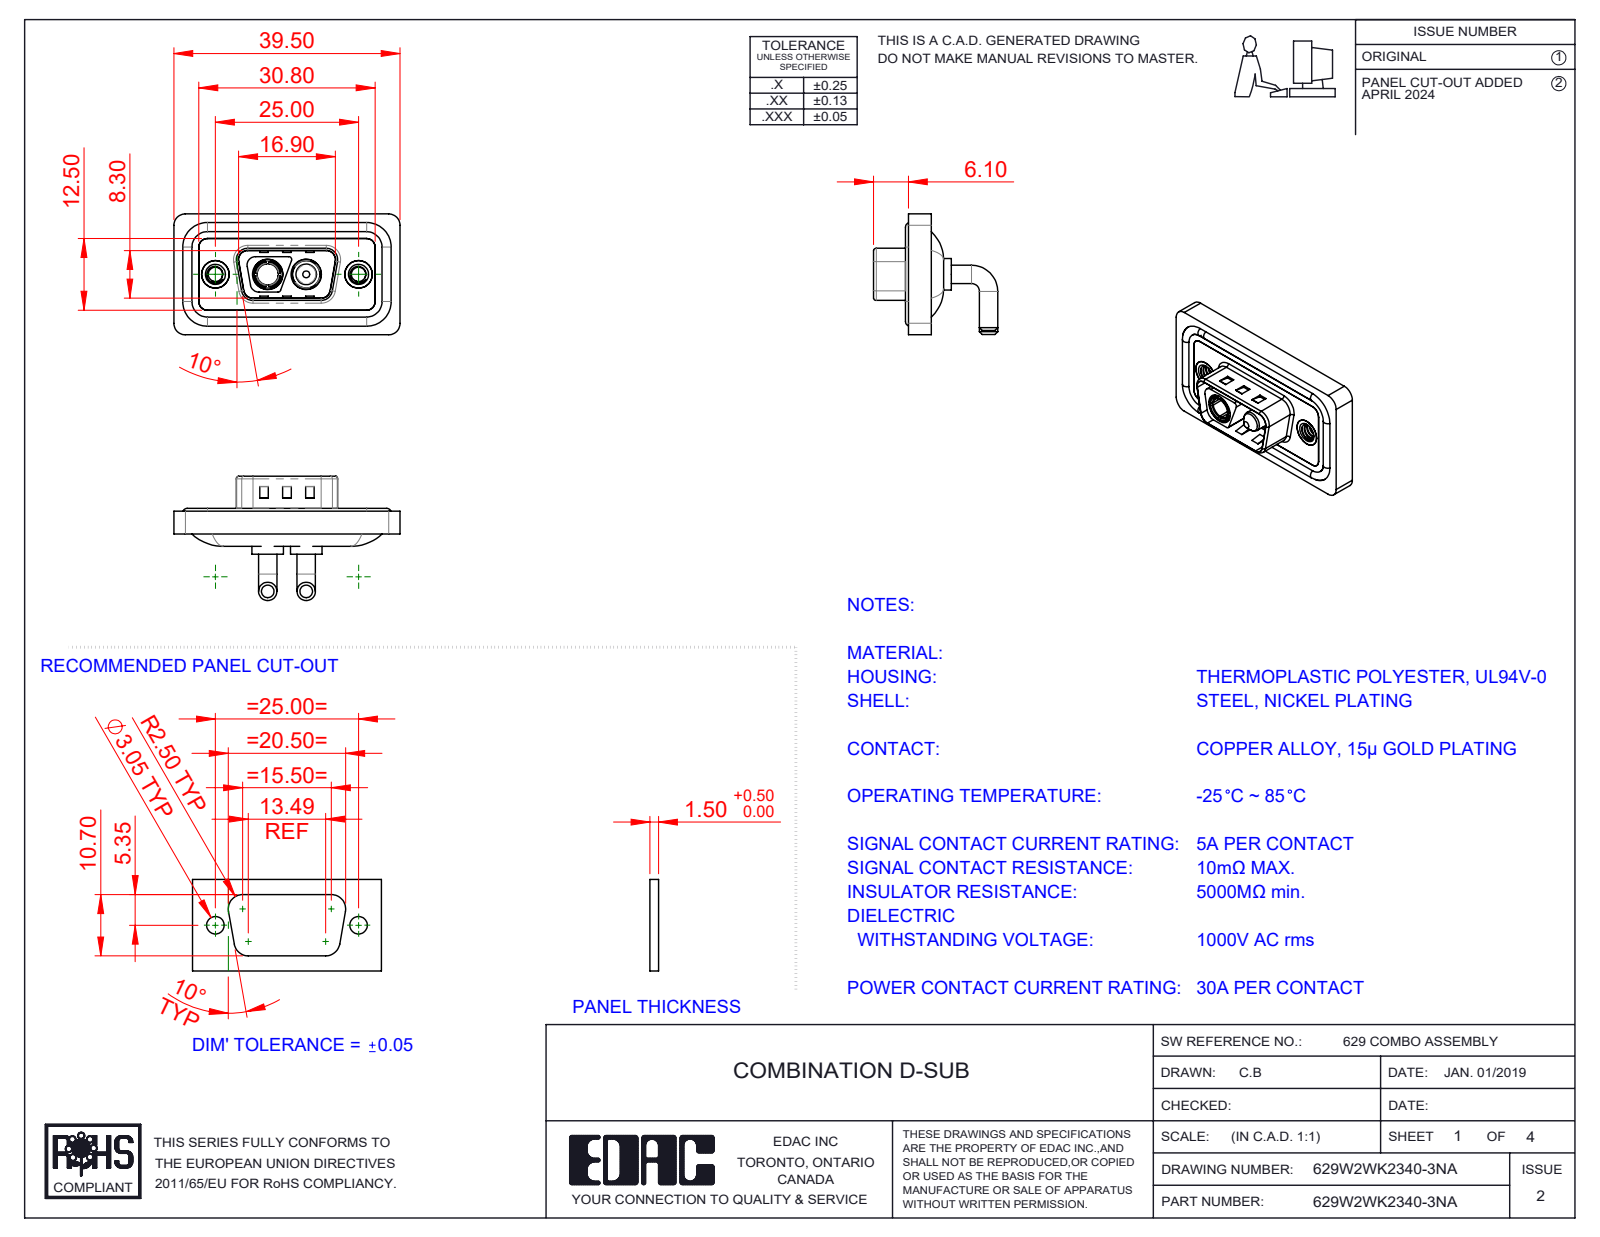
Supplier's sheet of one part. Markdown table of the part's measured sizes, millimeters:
| quantity | value |
| --- | --- |
| part name | 629Combo Shell Rear_09 Contacts; 629Combo Housing_2WK2; 629Combo Threaded Rivet_A; 629Combo Waterproof Housing_09 Contacts (+4 more) |
| STEP written by | SolidWorks 2023 (CONFIG_CONTROL_DESIGN) |
| units | millimeters |
| bodies | 11 solids, 536 faces (189 planar, 229 cylindrical, 118 other) |
| overall size | 39.5 × 21.7 × 21.1 |
| volume | 4 743 mm³ |
| surface area | 7 573 mm² |
| round holes (diameter × count) | 2.5 × 2, 4 × 2, 4.8 × 2, 4.85 × 2, 5 × 2, 5.3 × 2, 3.7 × 1 |
| round bosses / shafts (diameter × count) | 3.2 × 4, 1.6 × 4, 5.5 × 2, 5.2 × 2, 4.9 × 2, 4.75 × 2, 3.75 × 2, 4.96 × 1 |
| partial cylindrical surfaces (radius × count) | 1.5 × 20, 2 × 18, 0.5 × 10, 1.6 × 8, 0.25 × 4, 0.6 × 4, 0.65 × 4, 0.9 × 4 |
| main face-to-face distances | 0.4, 2.9, 1.1, 0.8, 2.1, 2.5, 3.1, 1.6, 4.5, 1.5 |
| hole center spacings | 9.14, 15.86, 6.72, 25 |
